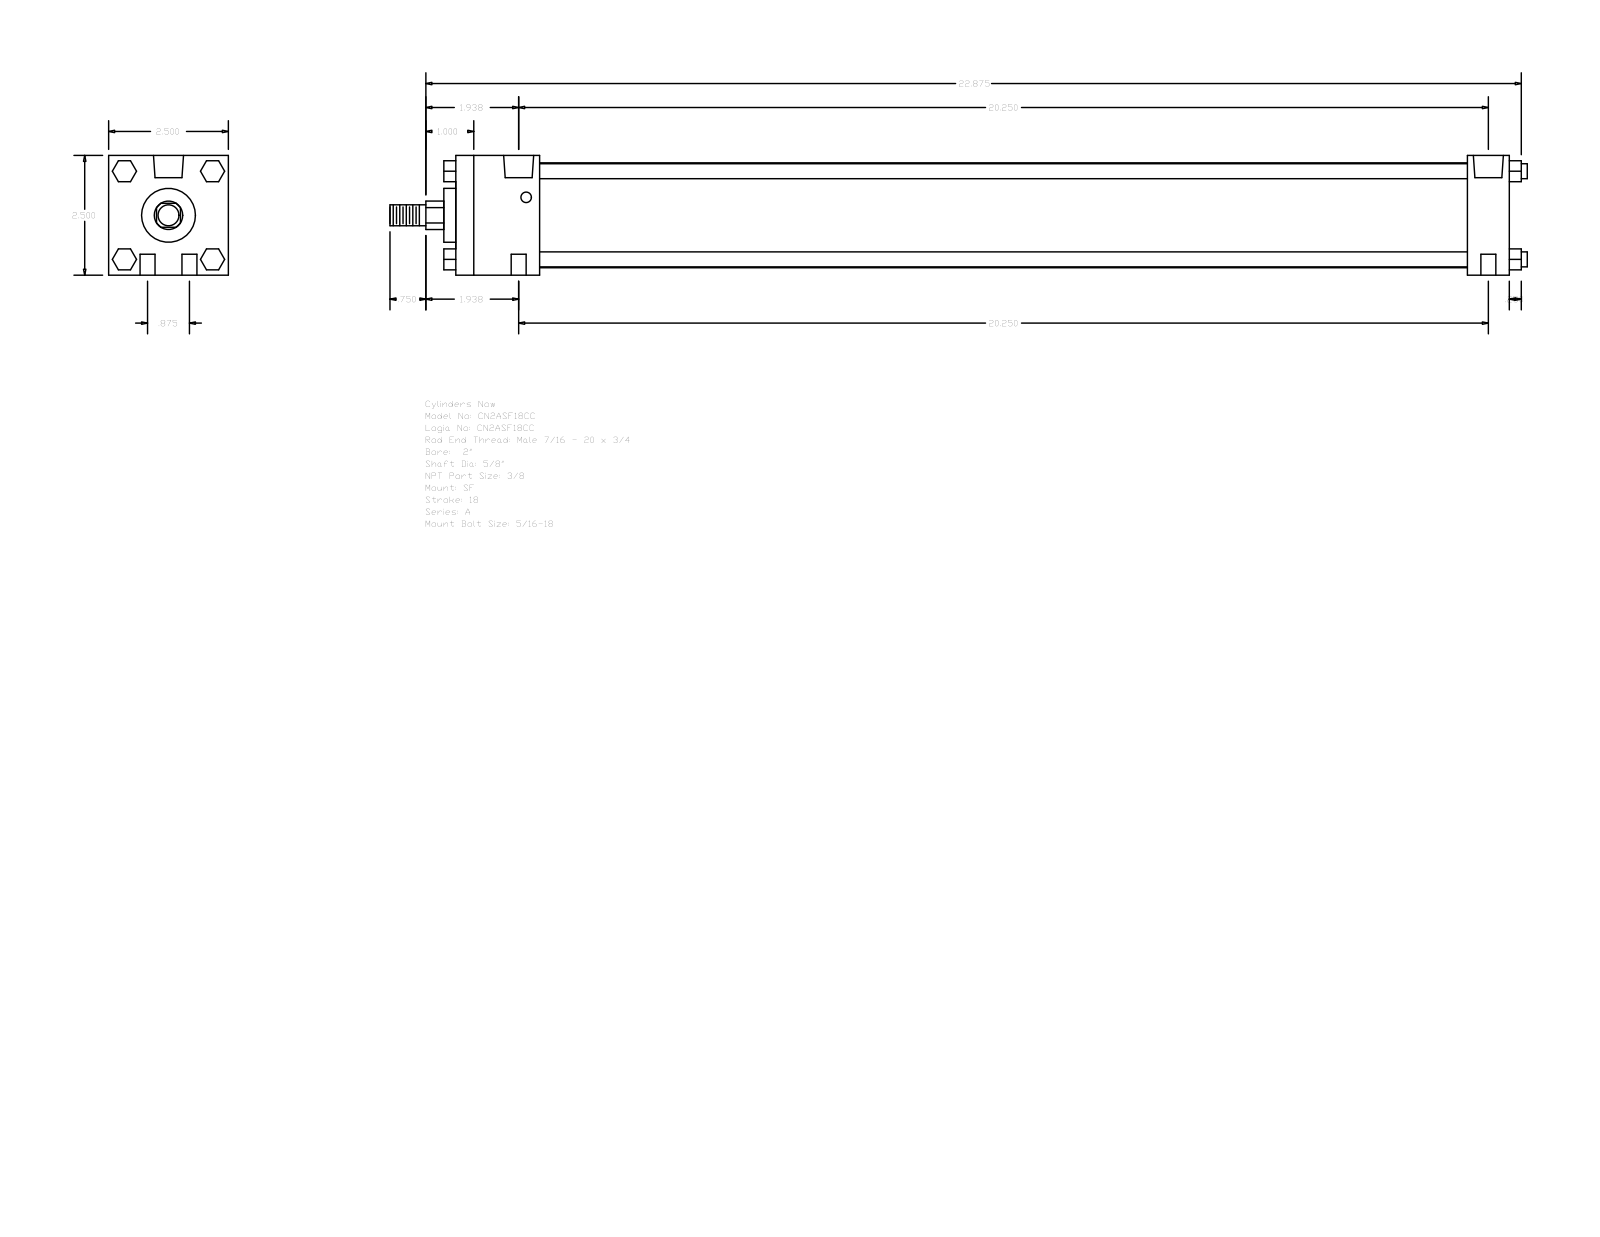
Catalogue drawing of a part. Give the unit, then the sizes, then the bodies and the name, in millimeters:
Units: millimetres
Overall size (bounding box): 603.25 × 63.5 × 63.5
Round holes (diameter × count): ⌀7.94 ×4, ⌀5.56 ×2, ⌀15.93 ×2
Round bosses / shafts (diameter × count): ⌀7.94 ×4, ⌀55.63 ×1, ⌀28.57 ×1, ⌀15.88 ×1, ⌀11.11 ×1
Partial cylindrical surfaces — rounded edges, fillets, slot ends (radius × count): R7.54 ×1
Main face-to-face distances: 63.5, 558.79, 536.57, 22.22, 44.45, 492.12, 514.34, 6.35, 565.14, 50.8
Hole centre spacings: 11.11, 514.47, 514.35, 22.22, 514.83, 506.4
Bodies: 0 solids, 124 faces (94 planar, 30 cylindrical, 0 other)
Part name (STEP PRODUCT): A_SF__0200_0.625
STEP written by: GSSL Pune (CONFIG_CONTROL_DESIGN)
